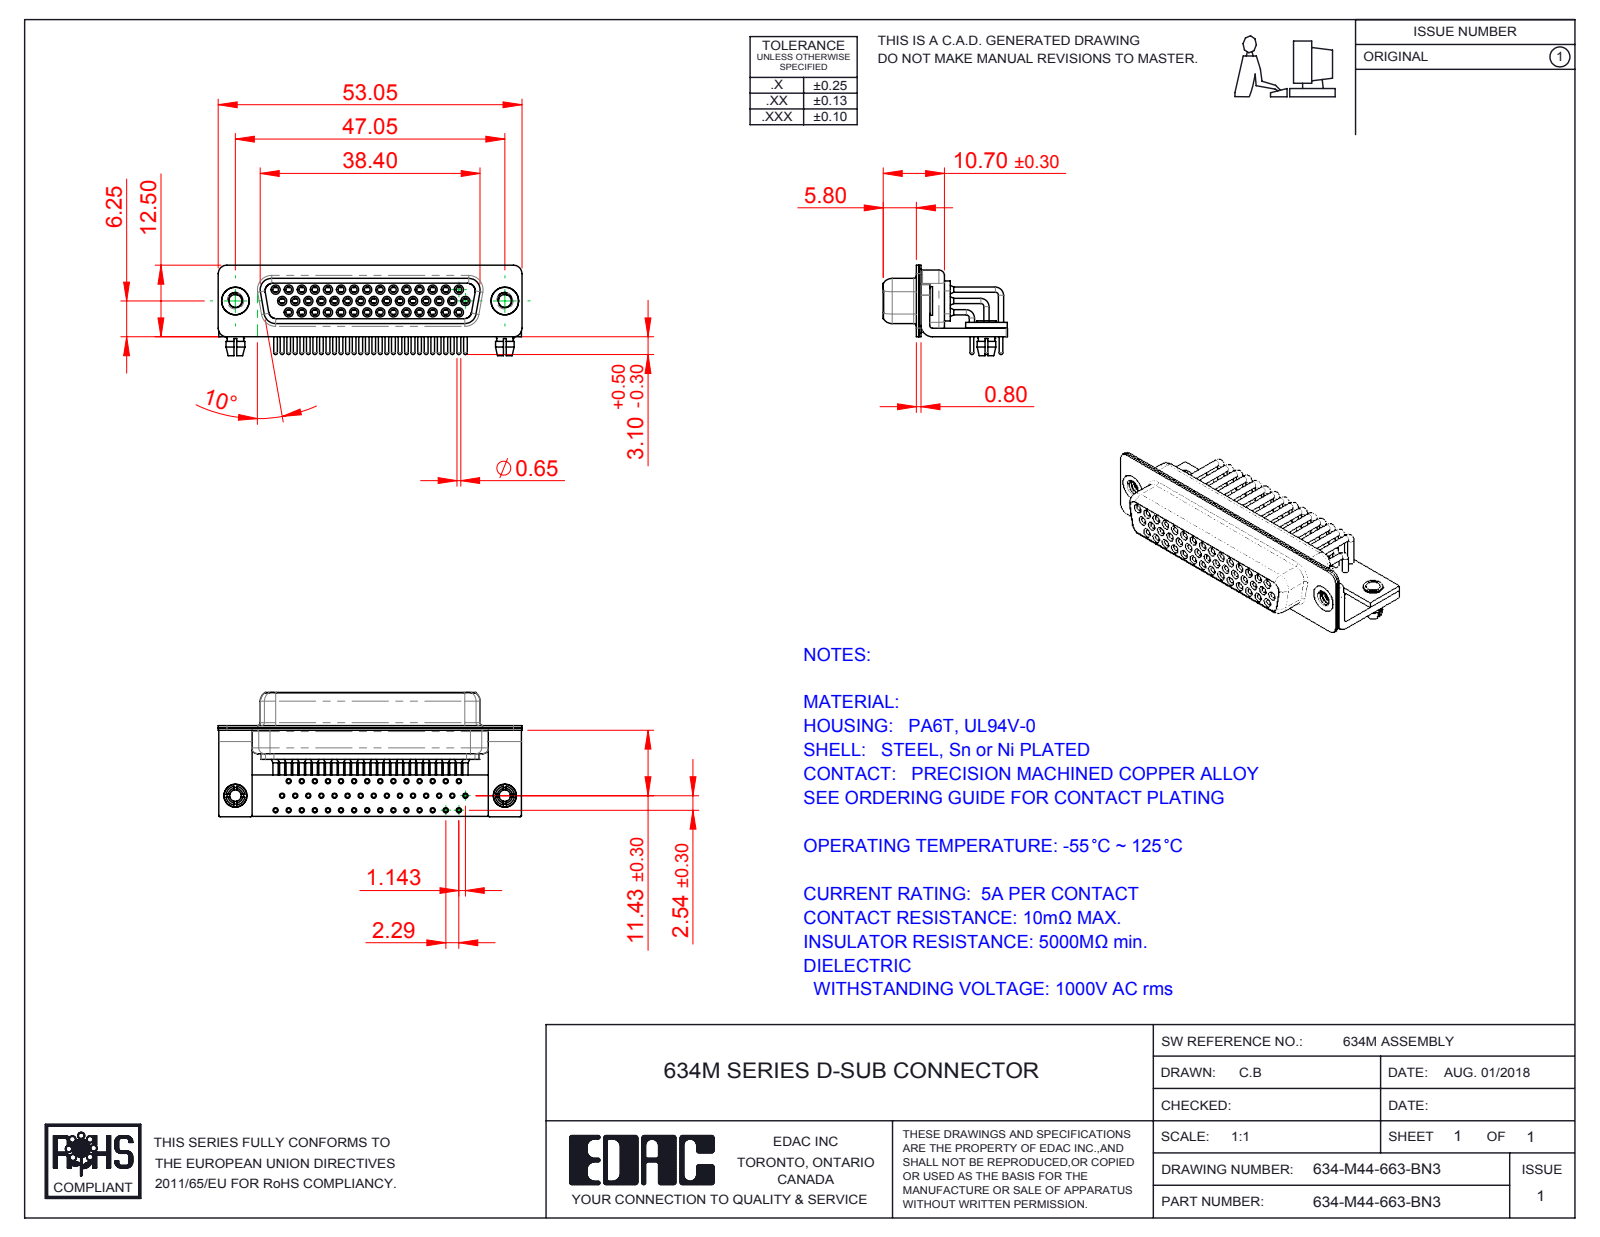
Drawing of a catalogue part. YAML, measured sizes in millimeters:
part_name: "634M Stabilizer Board_44 Contacts; 634-M44-663-BN3; 634M Contact Row 3; 634M Shell Rear_44 Contacts (+7 more)"
step_written_by: "SolidWorks 2016 (CONFIG_CONTROL_DESIGN)"
units: millimeters
bodies: {solids: 54, faces: 2841, planar: 801, cylindrical: 1291, other: 749}
overall_size: [53.05, 21.7, 15.8]
volume: 4503
surface_area: 14836
round_holes:
  - {diameter: 2, count: 46}
  - {diameter: 0.9, count: 44}
  - {diameter: 1, count: 44}
  - {diameter: 1.1, count: 44}
  - {diameter: 1.7, count: 44}
  - {diameter: 1.8, count: 44}
  - {diameter: 2.26, count: 2}
  - {diameter: 2.5, count: 2}
  - {diameter: 3.2, count: 2}
  - {diameter: 4, count: 2}
  - {diameter: 4.8, count: 2}
round_bosses_or_shafts:
  - {diameter: 1.6, count: 44}
  - {diameter: 1.5, count: 44}
  - {diameter: 0.9, count: 44}
  - {diameter: 0.65, count: 44}
  - {diameter: 5, count: 2}
  - {diameter: 4.9, count: 2}
  - {diameter: 4, count: 2}
  - {diameter: 3.4, count: 2}
partial_cylinders:
  - {radius: 0.25, count: 16}
  - {radius: 1.5, count: 16}
  - {radius: 2, count: 13}
  - {radius: 1.35, count: 8}
  - {radius: 1.6, count: 8}
  - {radius: 0.5, count: 5}
  - {radius: 0.6, count: 4}
  - {radius: 0.65, count: 4}
face_to_face_distances: [0.4, 2.3, 1, 1.9, 0.8, 9.35, 1.45, 8.95, 1.5, 0.85]
hole_center_spacings: [2.28, 2.29, 4.57, 6.86, 11.43, 3.96, 8.24, 9.14]
